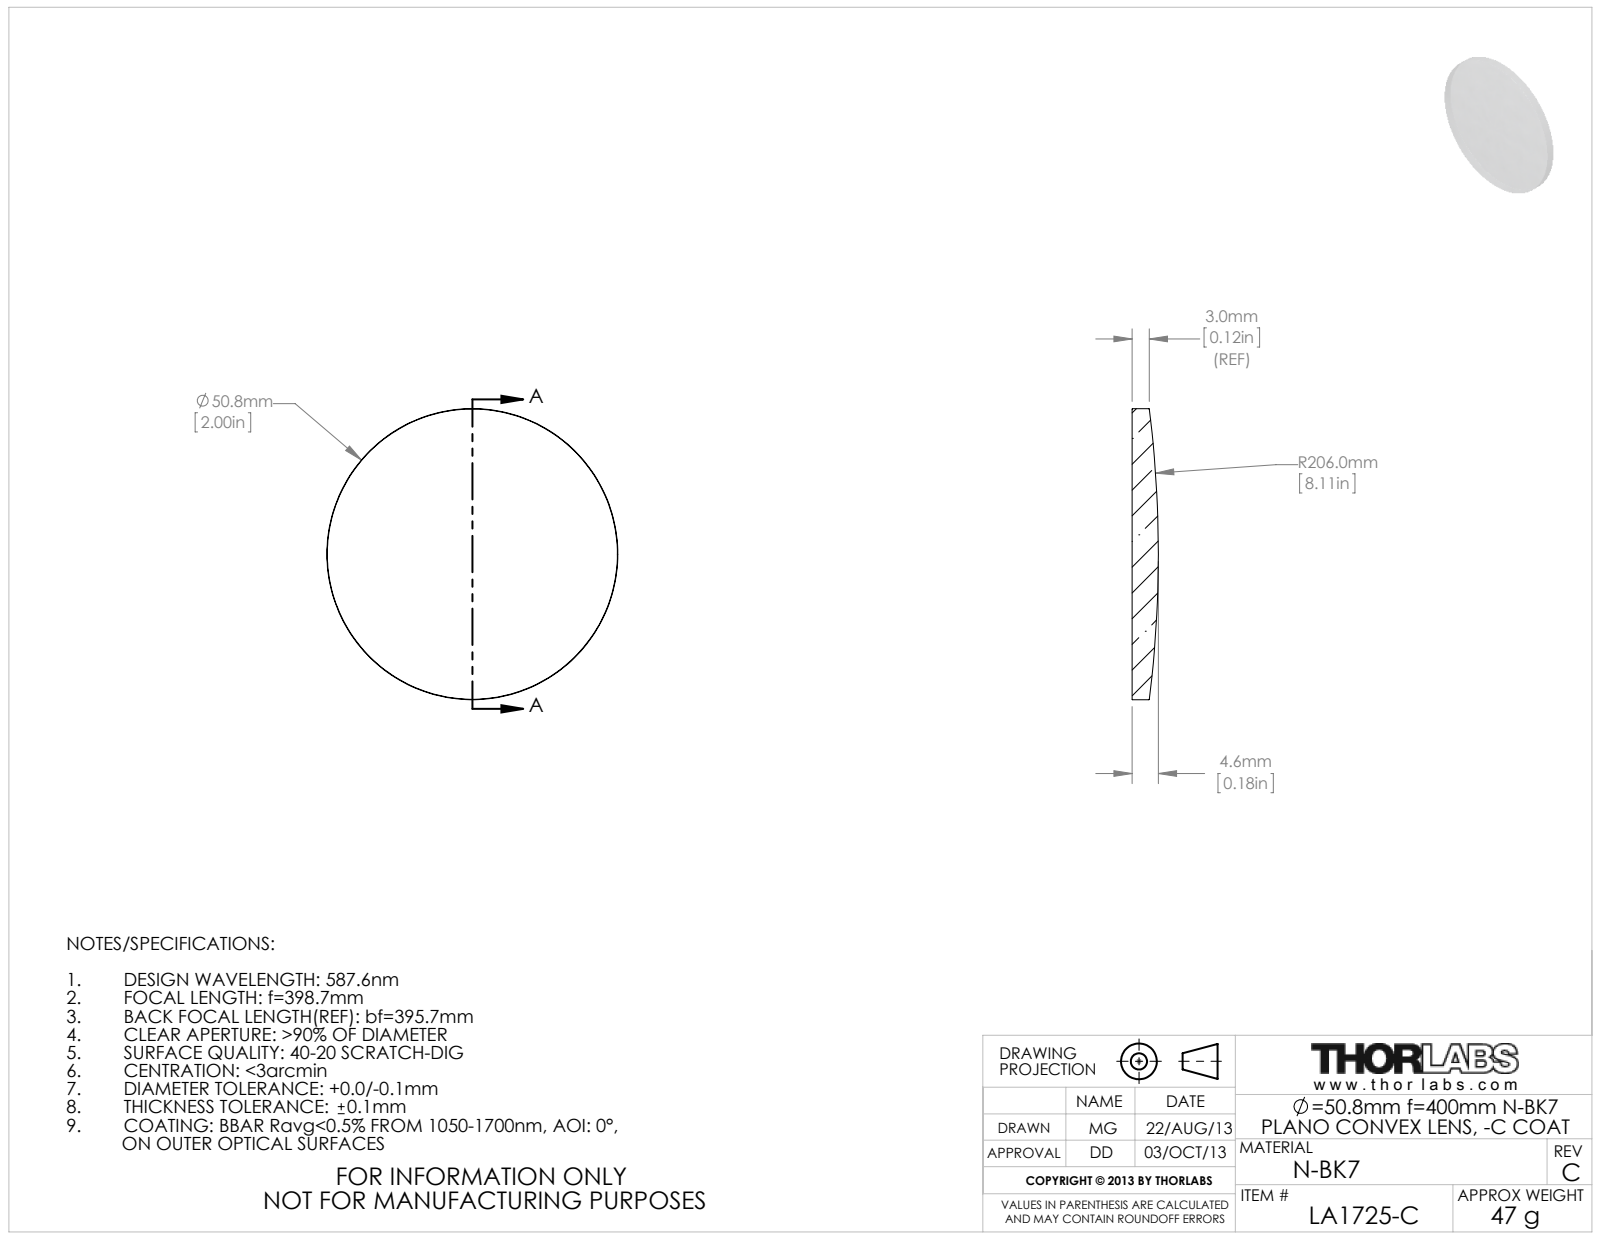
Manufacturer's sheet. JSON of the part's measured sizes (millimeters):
{"part_name": "4609-E0W", "step_written_by": "SolidWorks 2009 (AUTOMOTIVE_DESIGN)", "units": "millimeters", "bodies": {"solids": 0, "faces": 5, "planar": 1, "cylindrical": 2, "other": 2}, "overall_size": [50.8, 50.8, 4.57], "round_bosses_or_shafts": [[50.8, 1]]}
